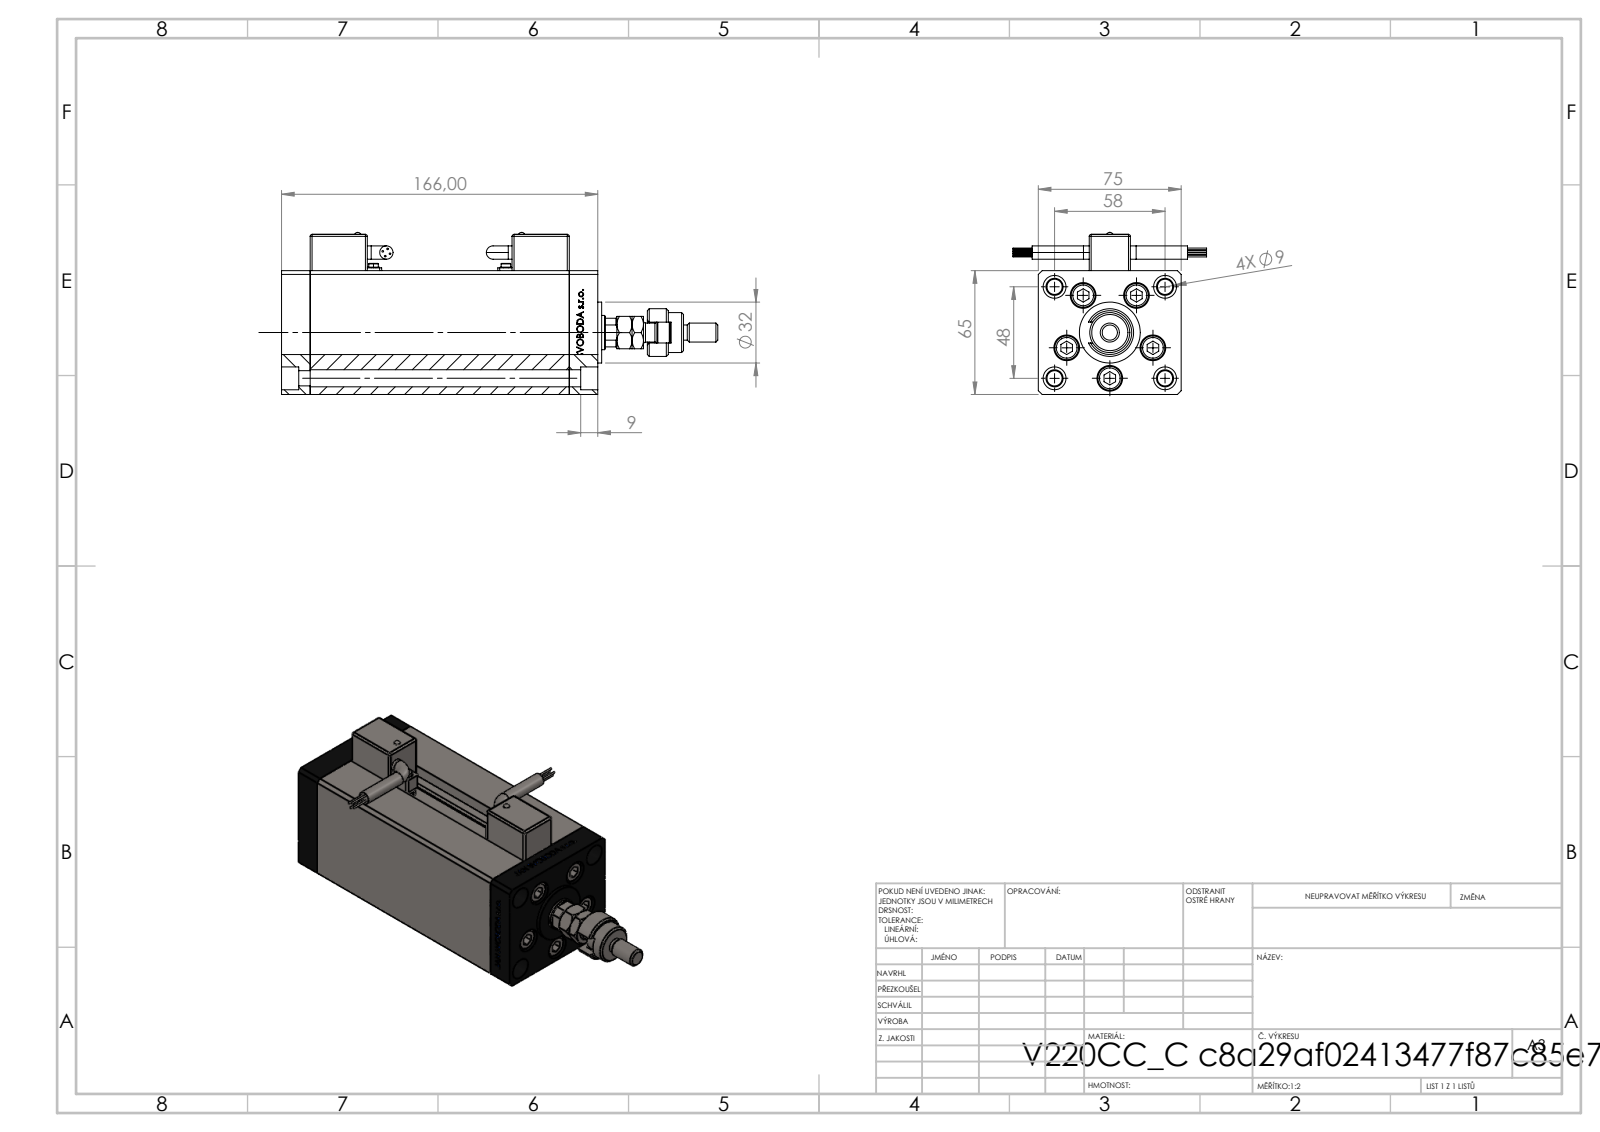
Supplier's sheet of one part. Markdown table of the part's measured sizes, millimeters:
| quantity | value |
| --- | --- |
| part name | V220C_VC_C; ALLEN BOLT; V220C_C MIDDLE; V220C FRONT (+4 more) |
| STEP written by | SolidWorks 2019 (CONFIG_CONTROL_DESIGN) |
| units | millimeters |
| bodies | 17 solids, 1468 faces (648 planar, 278 cylindrical, 542 other) |
| overall size | 229 × 101.6 × 85.1 |
| volume | 726 361 mm³ |
| surface area | 160 495 mm² |
| round holes (diameter × count) | 9 × 9, 13.5 × 5, 2 × 4, 8 × 4, 12 × 4, 13.16 × 4, 3.6 × 2, 5 × 2, 7 × 2, 8.5 × 1, 12.5 × 1, 18 × 1 |
| round bosses / shafts (diameter × count) | 0.85 × 8, 8 × 6, 12.5 × 4, 7 × 4, 6 × 2, 3.5 × 2, 2.5 × 2, 32 × 1 |
| partial cylindrical surfaces (radius × count) | 1 × 24, 4 × 4, 0.93 × 2, 5.5 × 1, 8.5 × 1, 8.75 × 1 |
| main face-to-face distances | 75, 65, 136, 15, 151, 166, 6.5, 48.3, 26.7, 58.5 |
| hole center spacings | 24, 37.64, 8.25, 15.67, 17.22, 21.26, 27.71, 28 |
